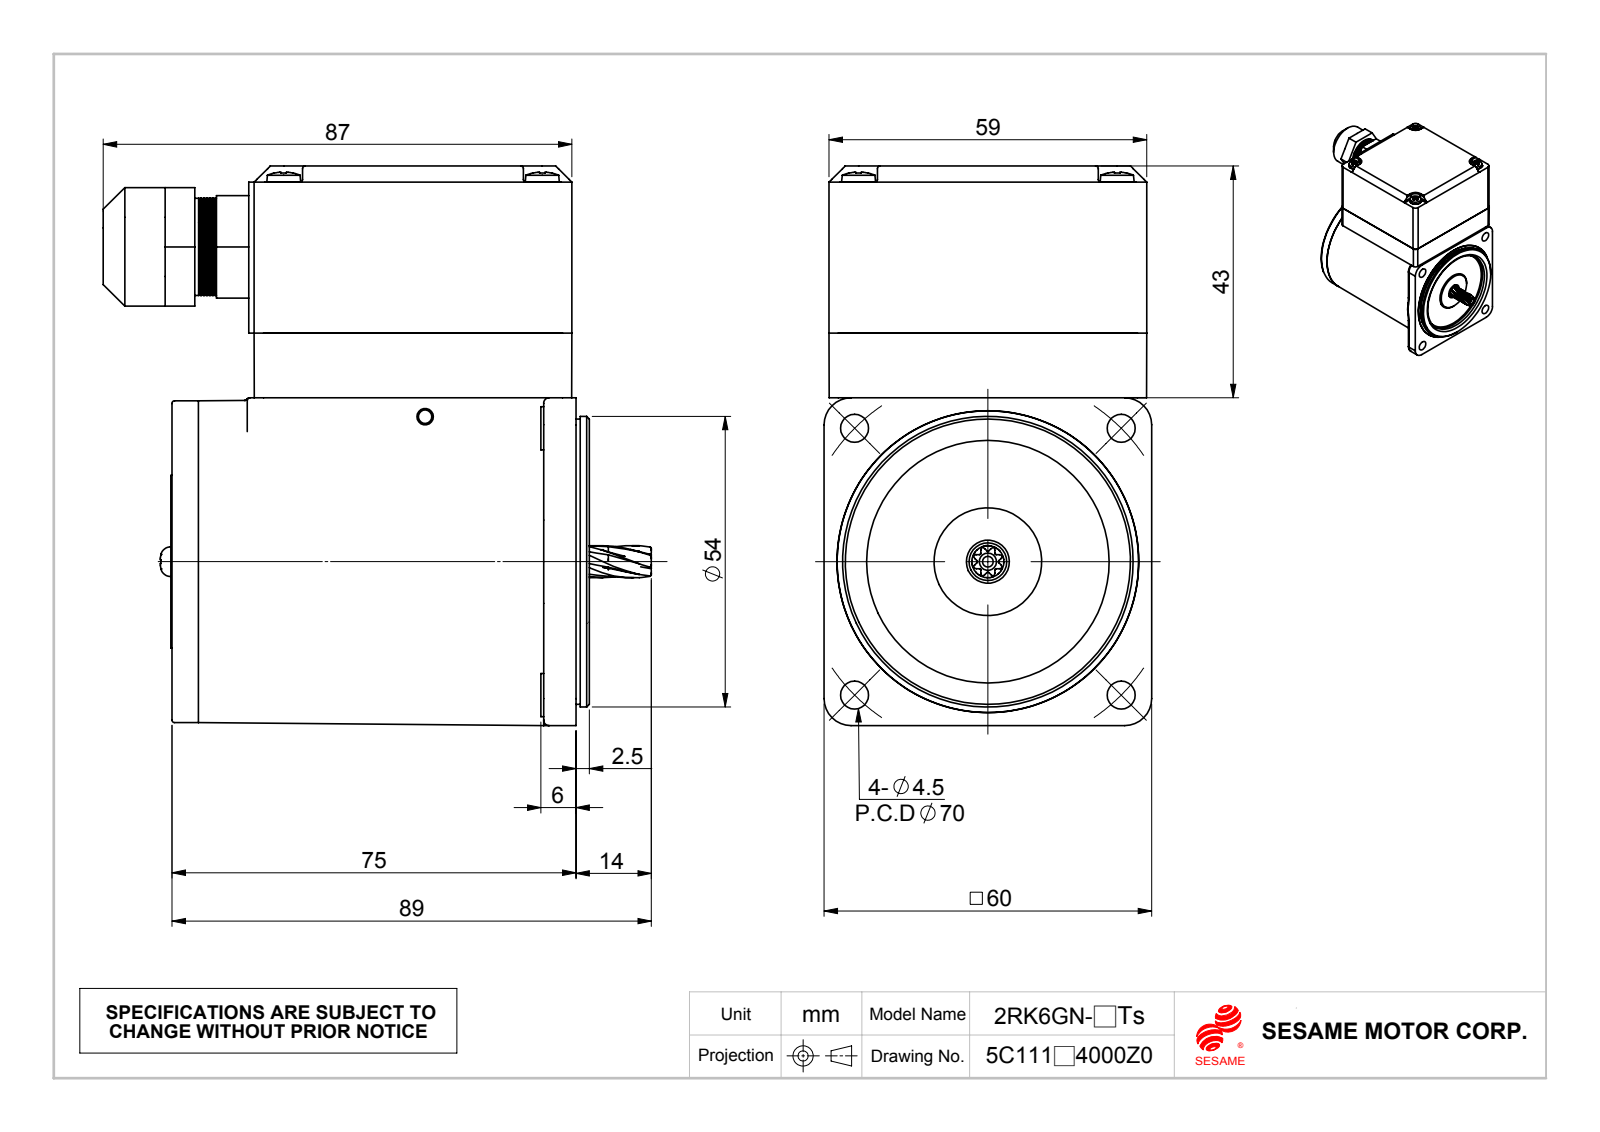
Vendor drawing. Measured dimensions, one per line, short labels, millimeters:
name: 펥짰웰찿M2즤32x1t_Default; 06GN_0成品; C254_Default; M206Ts-RK_2.成品 (+2 more)
written by: SolidWorks 2010 (CONFIG_CONTROL_DESIGN)
unit: mm
bodies: 14 solids, 2605 faces (239 planar, 864 cylindrical, 1502 other)
size: 103.8 × 101.75 × 60.8
volume: 218 416 mm³; area: 79 167 mm²
holes: 4× ⌀3.2, 4× ⌀3.3, 4× ⌀3.5, 4× ⌀3.9, 4× ⌀4.3, 4× ⌀5.2, 3× ⌀2.5, 2× ⌀4, 1× ⌀2, 1× ⌀7, 1× ⌀11, 1× ⌀12
bosses: 6× ⌀3, 4× ⌀8, 4× ⌀6.3, 2× ⌀5.5, 1× ⌀59.7, 1× ⌀53.93, 1× ⌀52.93, 1× ⌀32
rounds: 13× R0.5, 12× R2, 8× R0.3, 6× R4, 4× R1, 4× R1.5, 4× R3, 4× R3.5
face distances: 12, 0.75, 1, 43, 31, 1.5, 59, 73.7, 0.8, 5
hole spacings: 37.08, 12.25, 9.37, 17.32, 22.63, 22.75, 27.73, 35
